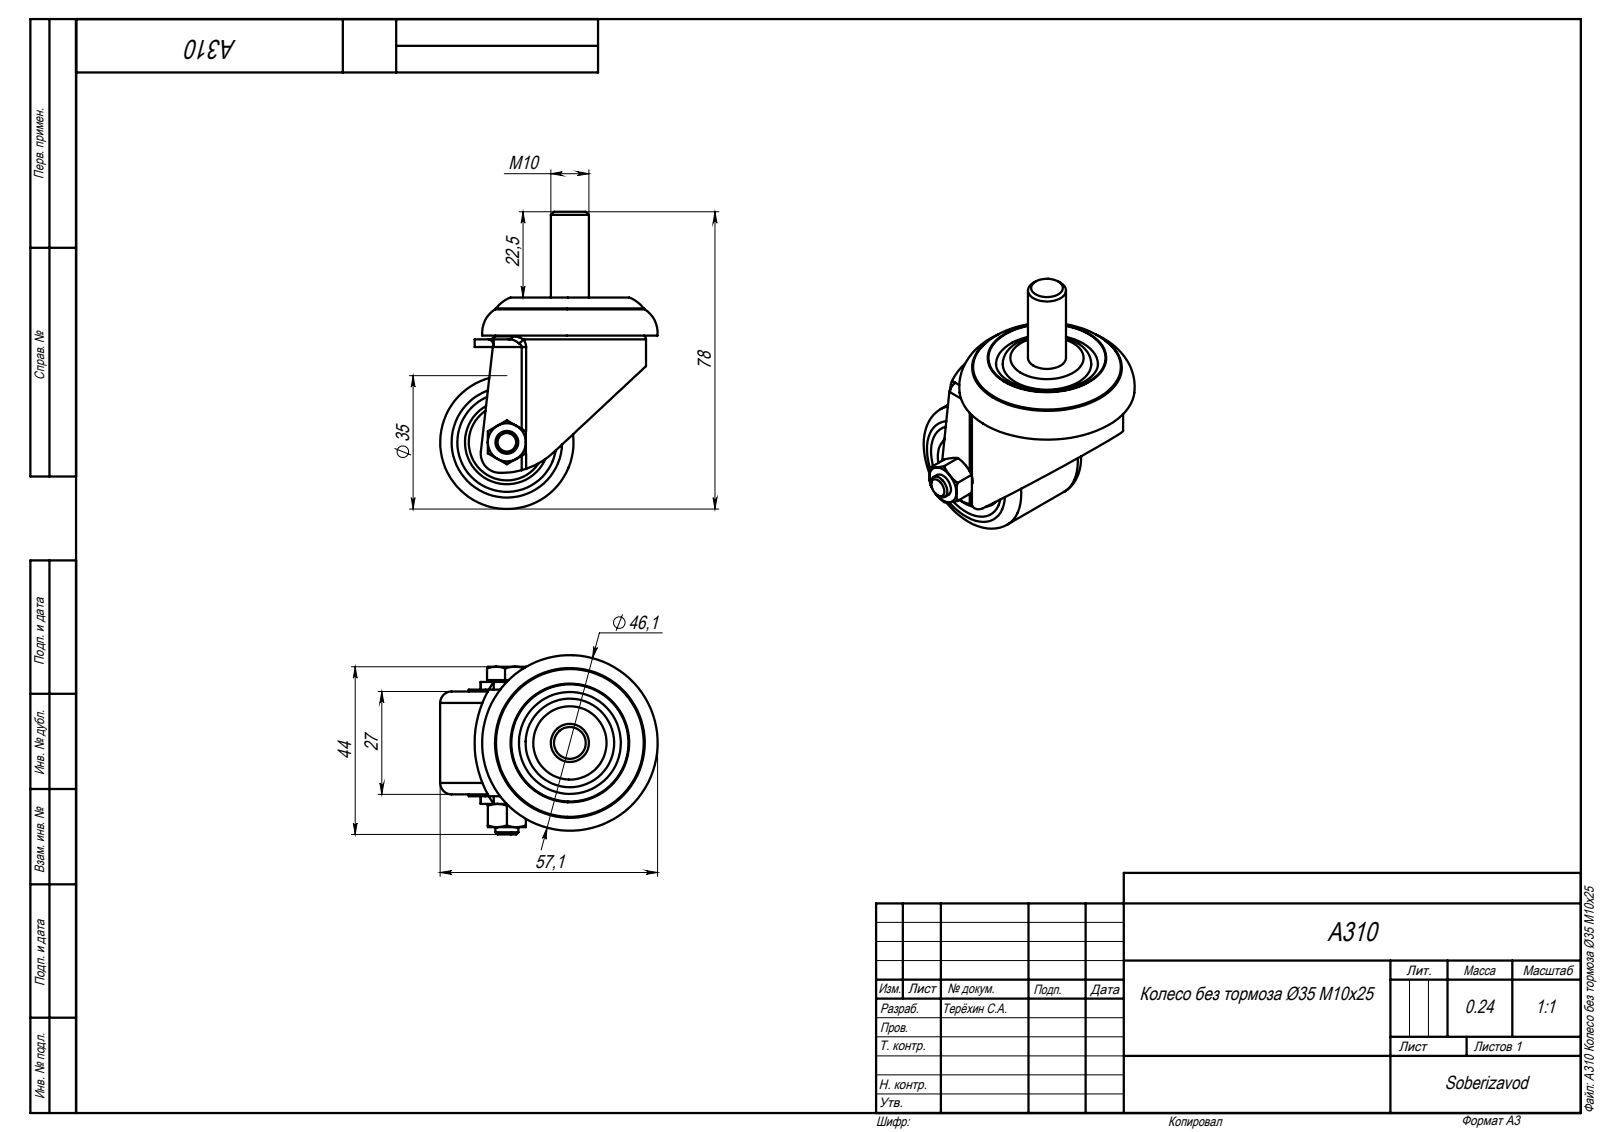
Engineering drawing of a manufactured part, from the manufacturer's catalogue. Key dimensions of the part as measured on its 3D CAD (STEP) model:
Part name (STEP PRODUCT): Основание_00; hex bolt gradeab_din_DIN EN 24014 - M6 x 40 x 18-N; Дно_00; socket head cap screw_din_DIN 912 M10 x 35 --- 35N (+5 more)
STEP written by: SolidWorks 2018 (AUTOMOTIVE_DESIGN)
Units: millimetres
Bodies: 9 solids, 204 faces (66 planar, 53 cylindrical, 85 other)
Overall size (bounding box): 77.99 × 57.08 × 47.04
Volume: 44 407 mm³ · Surface area: 25 635 mm²
Round holes (diameter × count): ⌀10 ×2, ⌀5 ×1, ⌀6 ×1, ⌀12 ×1, ⌀22 ×1
Round bosses / shafts (diameter × count): ⌀35 ×1, ⌀20 ×1, ⌀16 ×1
Partial cylindrical surfaces — rounded edges, fillets, slot ends (radius × count): R2 ×4, R20 ×2, R5 ×1, R18 ×1, R28.09 ×1
Main face-to-face distances: 2, 28, 4, 30, 7, 26, 9, 6.5, 32, 11
